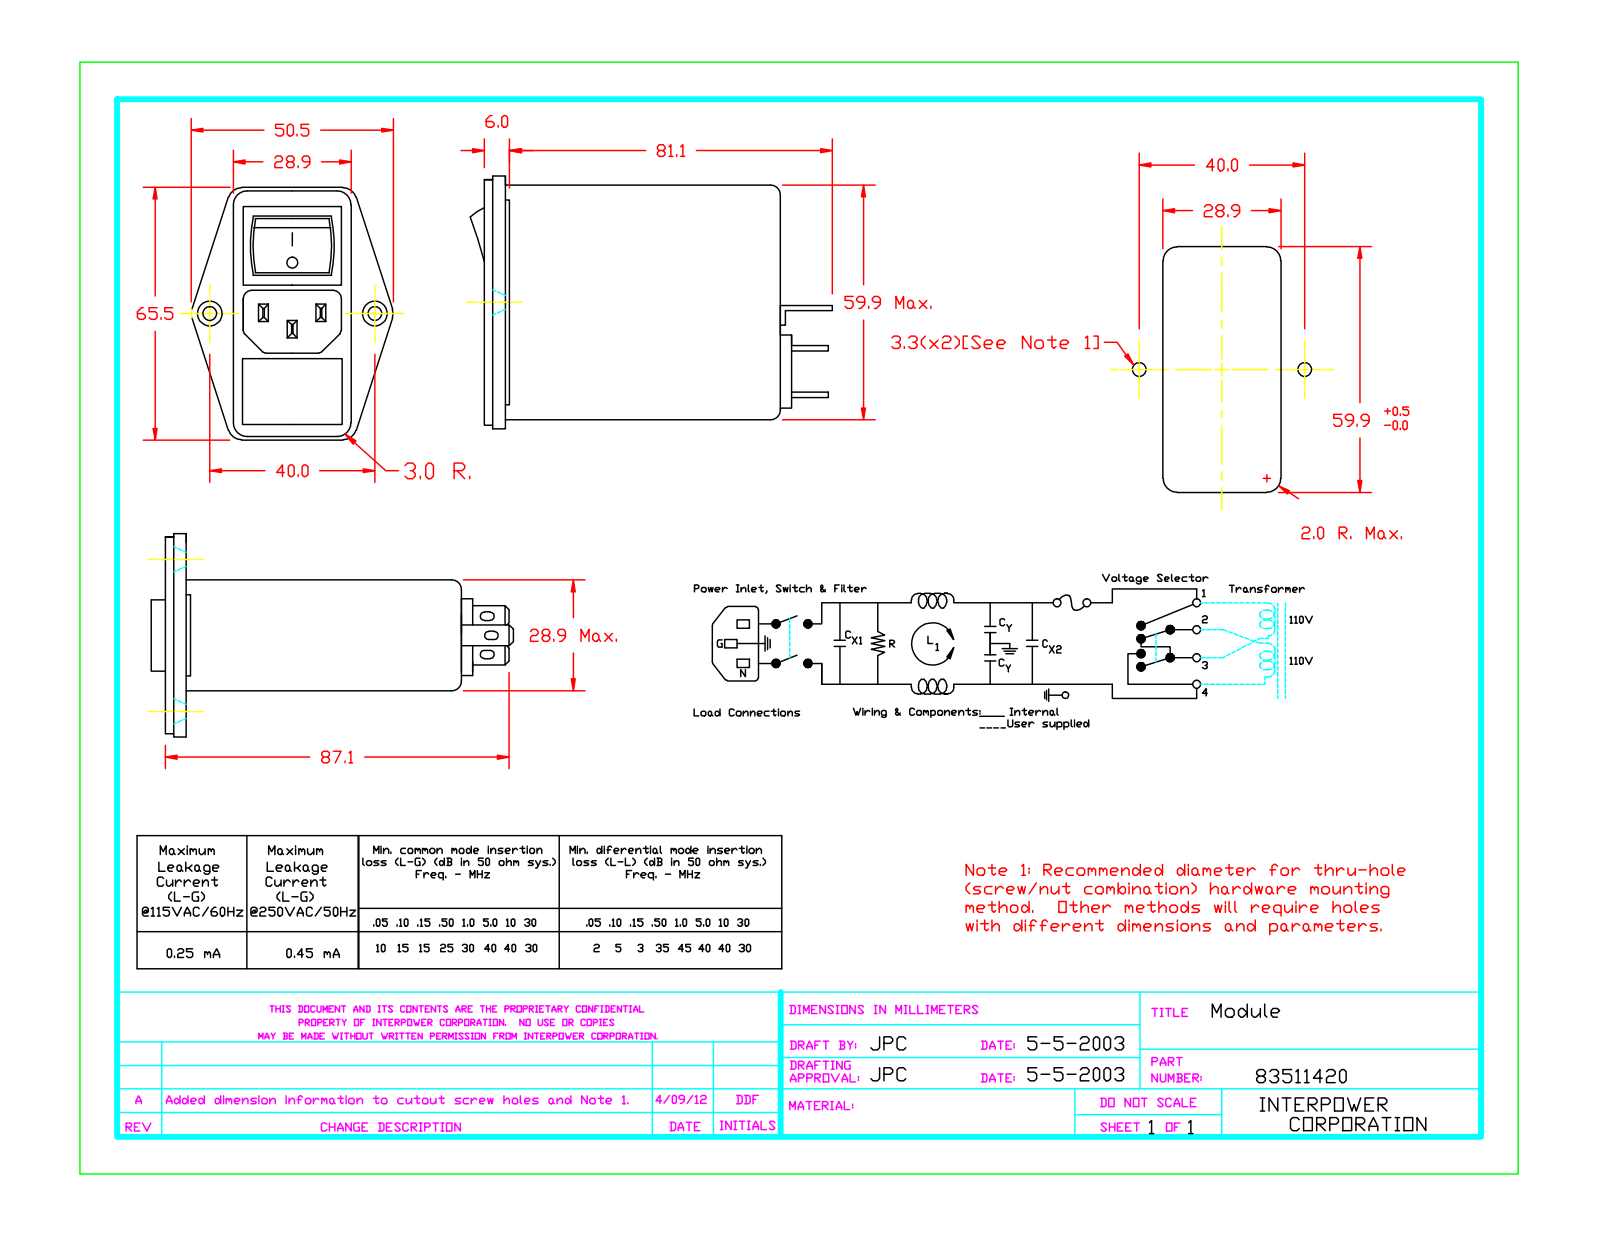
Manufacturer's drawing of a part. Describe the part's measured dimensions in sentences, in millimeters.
The part is named "83511420-R1". Its 3-D file was written by "SolidWorks 2007 (CONFIG_CONTROL_DESIGN)". It is 1 solid with 340 faces: 221 planar, 86 cylindrical and 33 other. Overall it measures 90.45 by 65.5 by 50.5 millimeters. Its volume is 128 292 cubic millimeters and its surface area 22 427 square millimeters. Round holes: 2 of diameter 3.5, 2 of diameter 4, 1 of diameter 3. Round bosses or shafts: 1 of diameter 2. Partial cylindrical surfaces (rounded edges, fillets, slot ends): 12 of radius 0.5, 9 of radius 0.25, 6 of radius 1, 4 of radius 0.85, 4 of radius 1.45, 4 of radius 1.5, 4 of radius 2, 4 of radius 3. The main face-to-face distances are 28.9, 60.4, 1, 75, 2, 69, 73, 4, 70, 6. The hole center spacings are 40.
